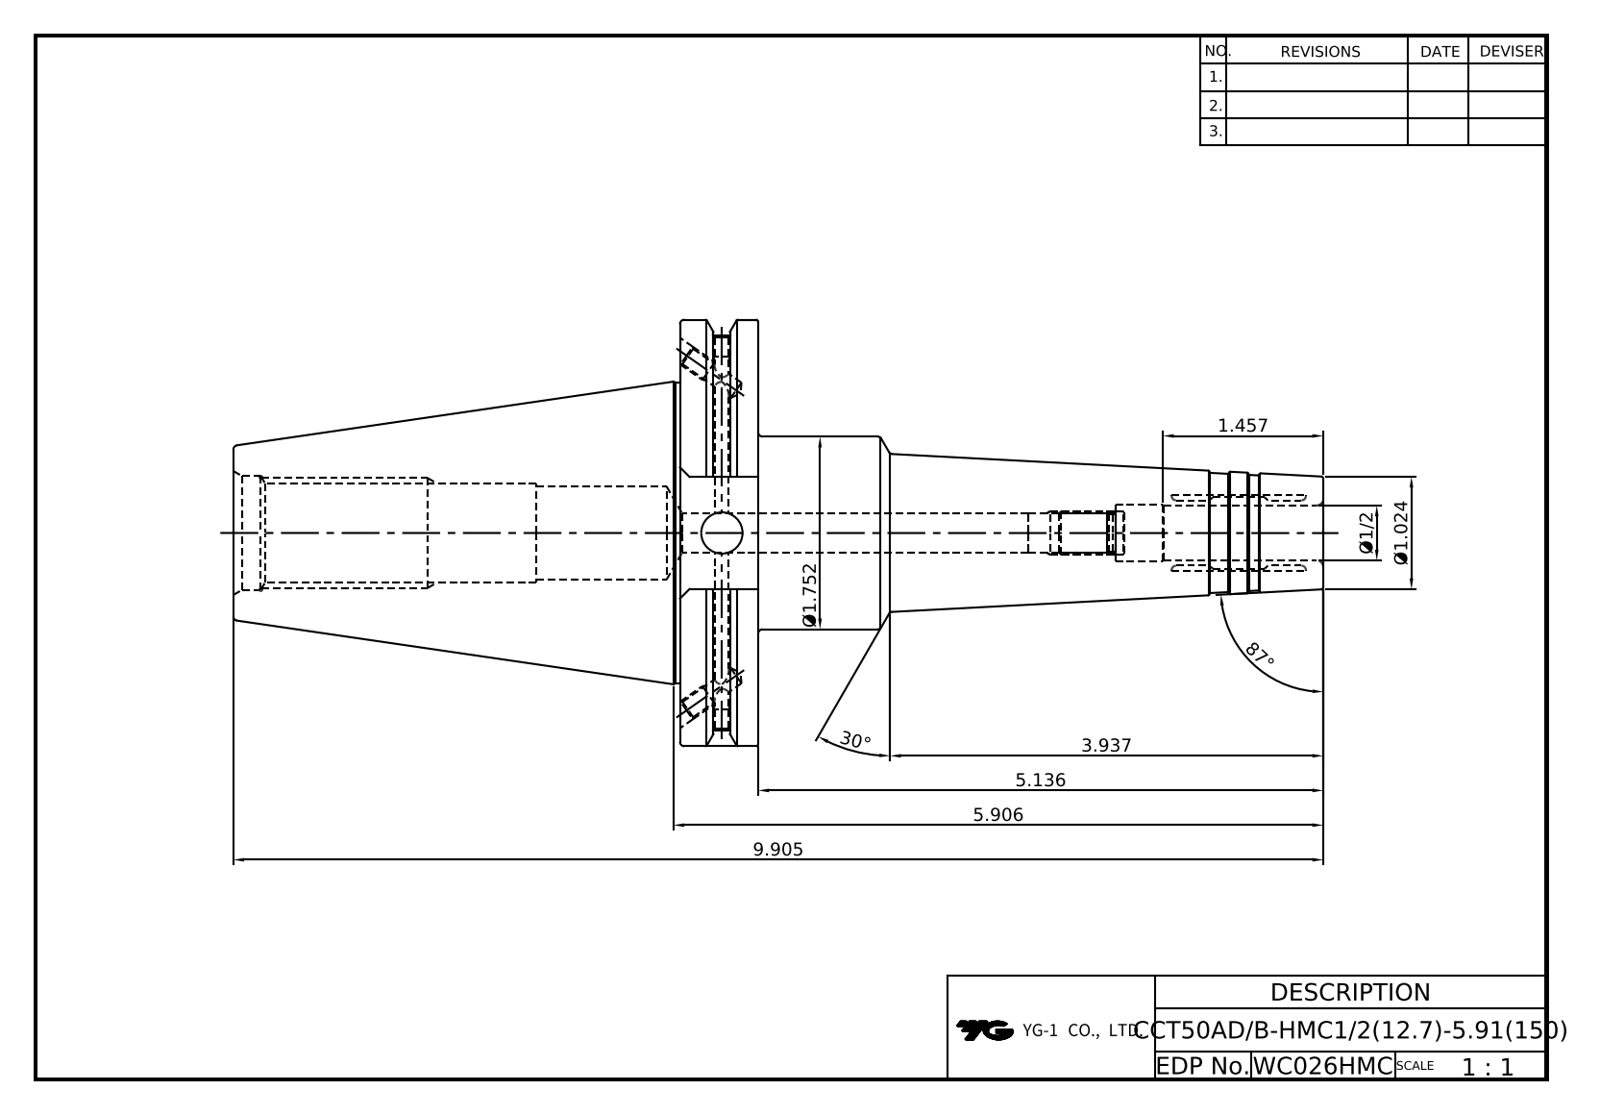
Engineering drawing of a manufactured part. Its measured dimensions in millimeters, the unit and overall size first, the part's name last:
Units: millimetres
Overall size (bounding box): 251.6 × 98.42 × 94.69
Round holes (diameter × count): ⌀3.24 ×2, ⌀4.13 ×2, ⌀4.2 ×2, ⌀5 ×2, ⌀8.92 ×1, ⌀9.53 ×1, ⌀12 ×1, ⌀12.5 ×1, ⌀21.5 ×1, ⌀21.97 ×1, ⌀26.2 ×1
Round bosses / shafts (diameter × count): ⌀98.42 ×1, ⌀91.29 ×1, ⌀69.25 ×1, ⌀44.5 ×1
Main face-to-face distances: 17.55, 103.1, 120.65, 73.03, 251.6, 148.5, 130.95, 25.9, 103.5, 0.4
Volume: 443 697 mm³ · Surface area: 62 213 mm²
Bodies: 1 solid, 100 faces (38 planar, 27 cylindrical, 35 other)
Part name (STEP PRODUCT): LO-CCT50ADB-HMC12.5-150
STEP written by: Autodesk Inventor 2024 (AUTOMOTIVE_DESIGN)
